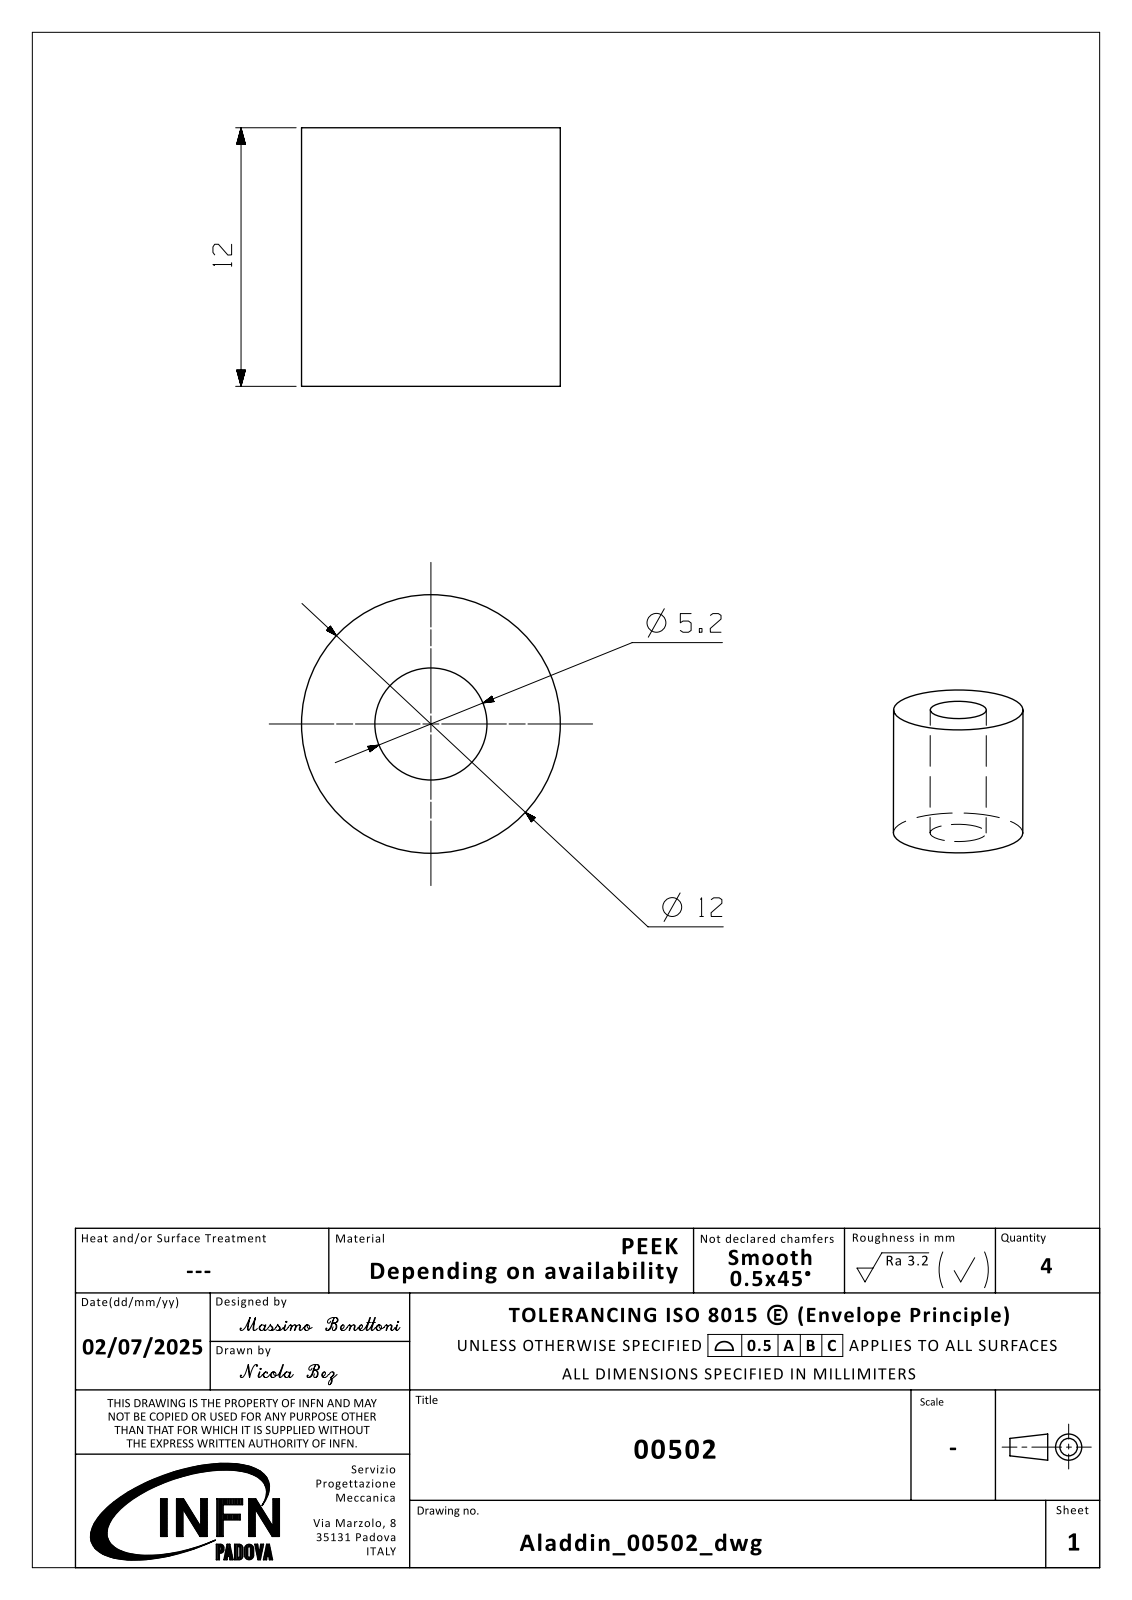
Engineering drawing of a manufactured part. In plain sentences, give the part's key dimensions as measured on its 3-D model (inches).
The part is named "IR3_00000502_objects". Its 3-D file was written by "SIEMENS PLM Software NX2306.9102 (AUTOMOTIVE_DESIGN)". It is 1 solid with 4 faces: 2 planar, 2 cylindrical and 0 other. Overall it measures 0.472 by 0.472 by 0.472 inches. Its volume is 0.067 cubic inches and its surface area 1.29 square inches. Round holes: 1 of diameter 0.205. Round bosses or shafts: 1 of diameter 0.472. The main face-to-face distances are 0.472.
